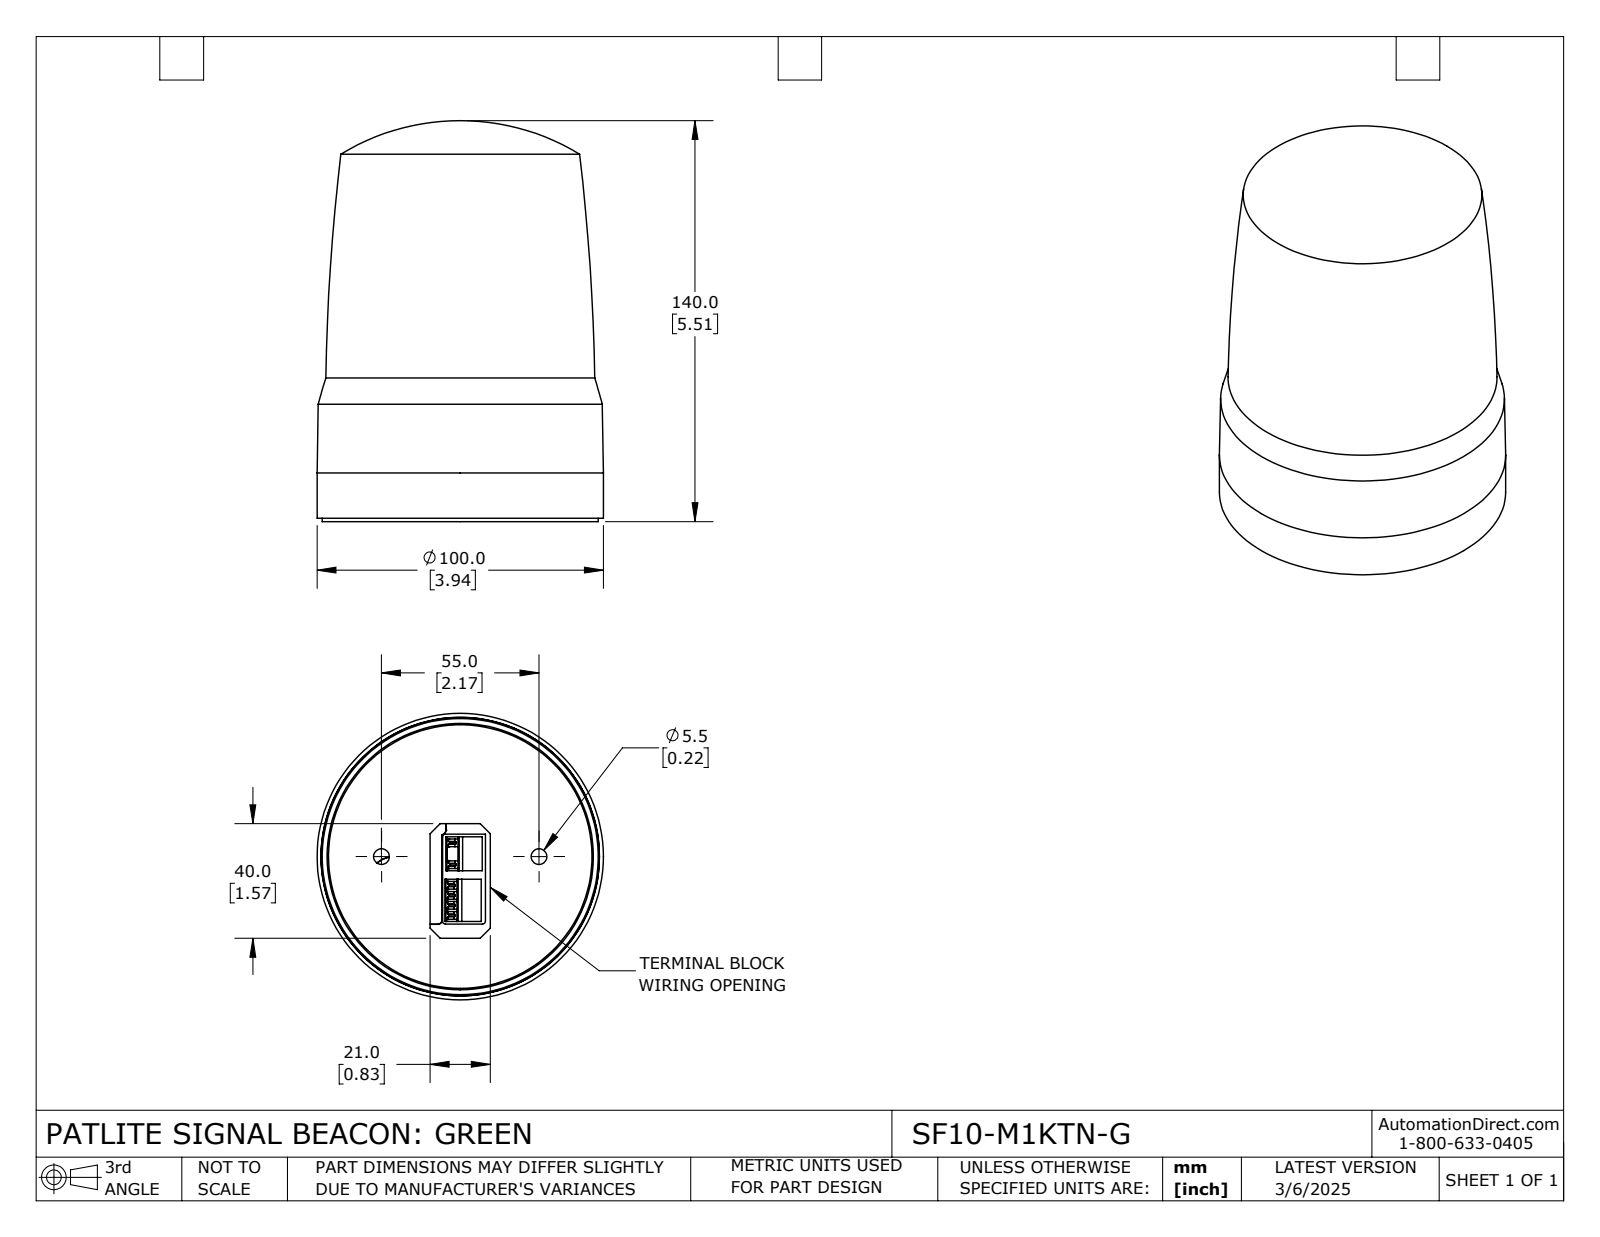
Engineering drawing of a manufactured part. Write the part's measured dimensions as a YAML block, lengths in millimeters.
part_name: "SF10-M1KTN-G"
step_written_by: "SolidWorks 2024 (CONFIG_CONTROL_DESIGN)"
units: millimeters
bodies: {solids: 2, faces: 268, planar: 183, cylindrical: 29, other: 56}
overall_size: [140, 100, 100]
volume: 857676
surface_area: 76986
round_holes:
  - {diameter: 5.5, count: 2}
  - {diameter: 13, count: 2}
  - {diameter: 93, count: 1}
  - {diameter: 95.6, count: 1}
round_bosses_or_shafts:
  - {diameter: 100, count: 1}
  - {diameter: 96.4, count: 1}
  - {diameter: 94.5, count: 1}
  - {diameter: 93.2, count: 1}
  - {diameter: 92, count: 1}
partial_cylinders:
  - {radius: 0.3, count: 2}
  - {radius: 44.32, count: 1}
  - {radius: 44.75, count: 1}
face_to_face_distances: [6.3, 14.7, 8.4, 1.5, 6.9, 13.2, 12.6, 3.15, 4.4, 7]
hole_center_spacings: [27.5, 55]
